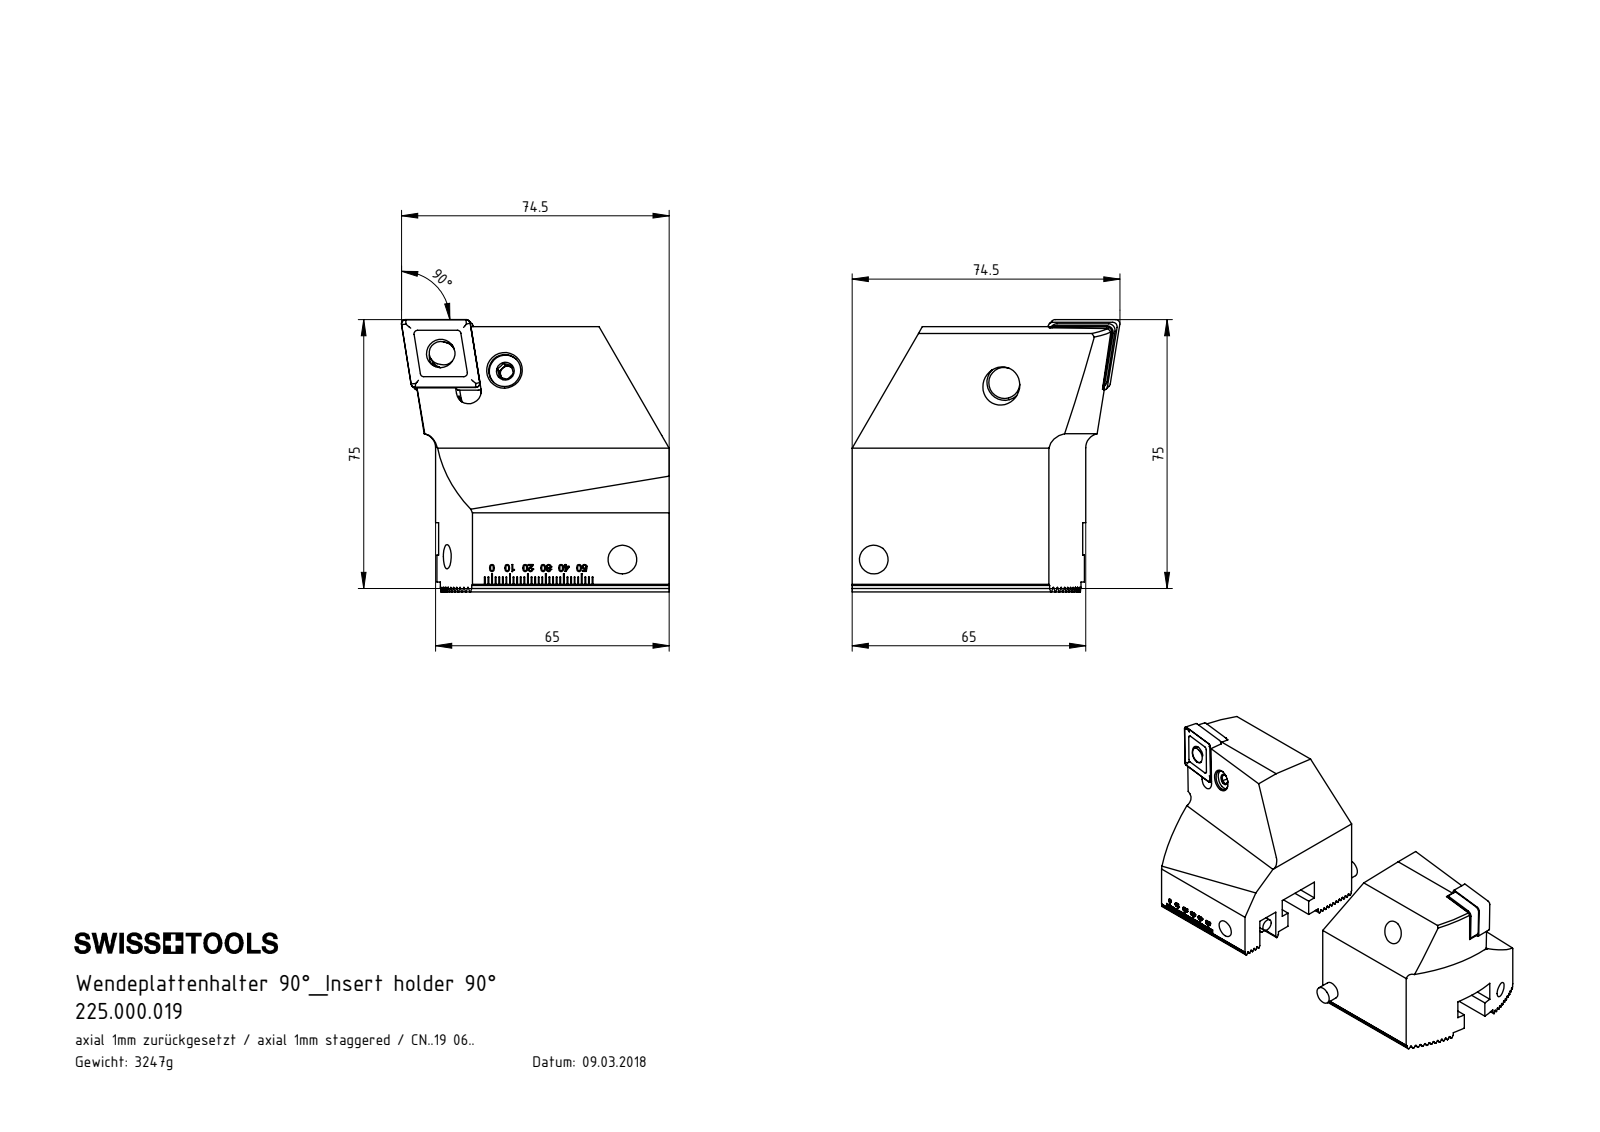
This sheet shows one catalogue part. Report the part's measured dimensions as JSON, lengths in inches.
{"part_name": "ISO 4028 - M8 x 35; WCF-ER3.101.000_A; 225.000.019; WCF-ER1.101.000 (+6 more)", "step_written_by": "SolidWorks 2017 (CONFIG_CONTROL_DESIGN)", "units": "inches", "bodies": {"solids": 16, "faces": 1300, "planar": 784, "cylindrical": 170, "other": 346}, "overall_size": [7.876, 3.304, 2.984], "volume_in3": 25.04, "surface_area_in2": 113.8, "round_holes": [[0.315, 4], [0.268, 2], [0.313, 2], [0.354, 2], [0.378, 2], [0.402, 2]], "round_bosses_or_shafts": [[0.394, 2], [0.39, 2], [0.339, 2], [0.315, 2], [0.217, 2], [0.175, 2]], "partial_cylinders_radius": [[0.006, 22], [0.047, 8], [0.071, 8], [0.163, 8], [0.185, 3], [0.122, 2], [0.138, 2], [0.144, 2]], "face_to_face_distances": [0.068, 0.273, 0.341, 2.756, 0.136, 0.205, 1.637, 1.705, 0.965, 1.791], "hole_center_spacings": [0.276, 0.729, 2.756, 0.012, 0.013, 0.74, 0.741, 1.575]}
